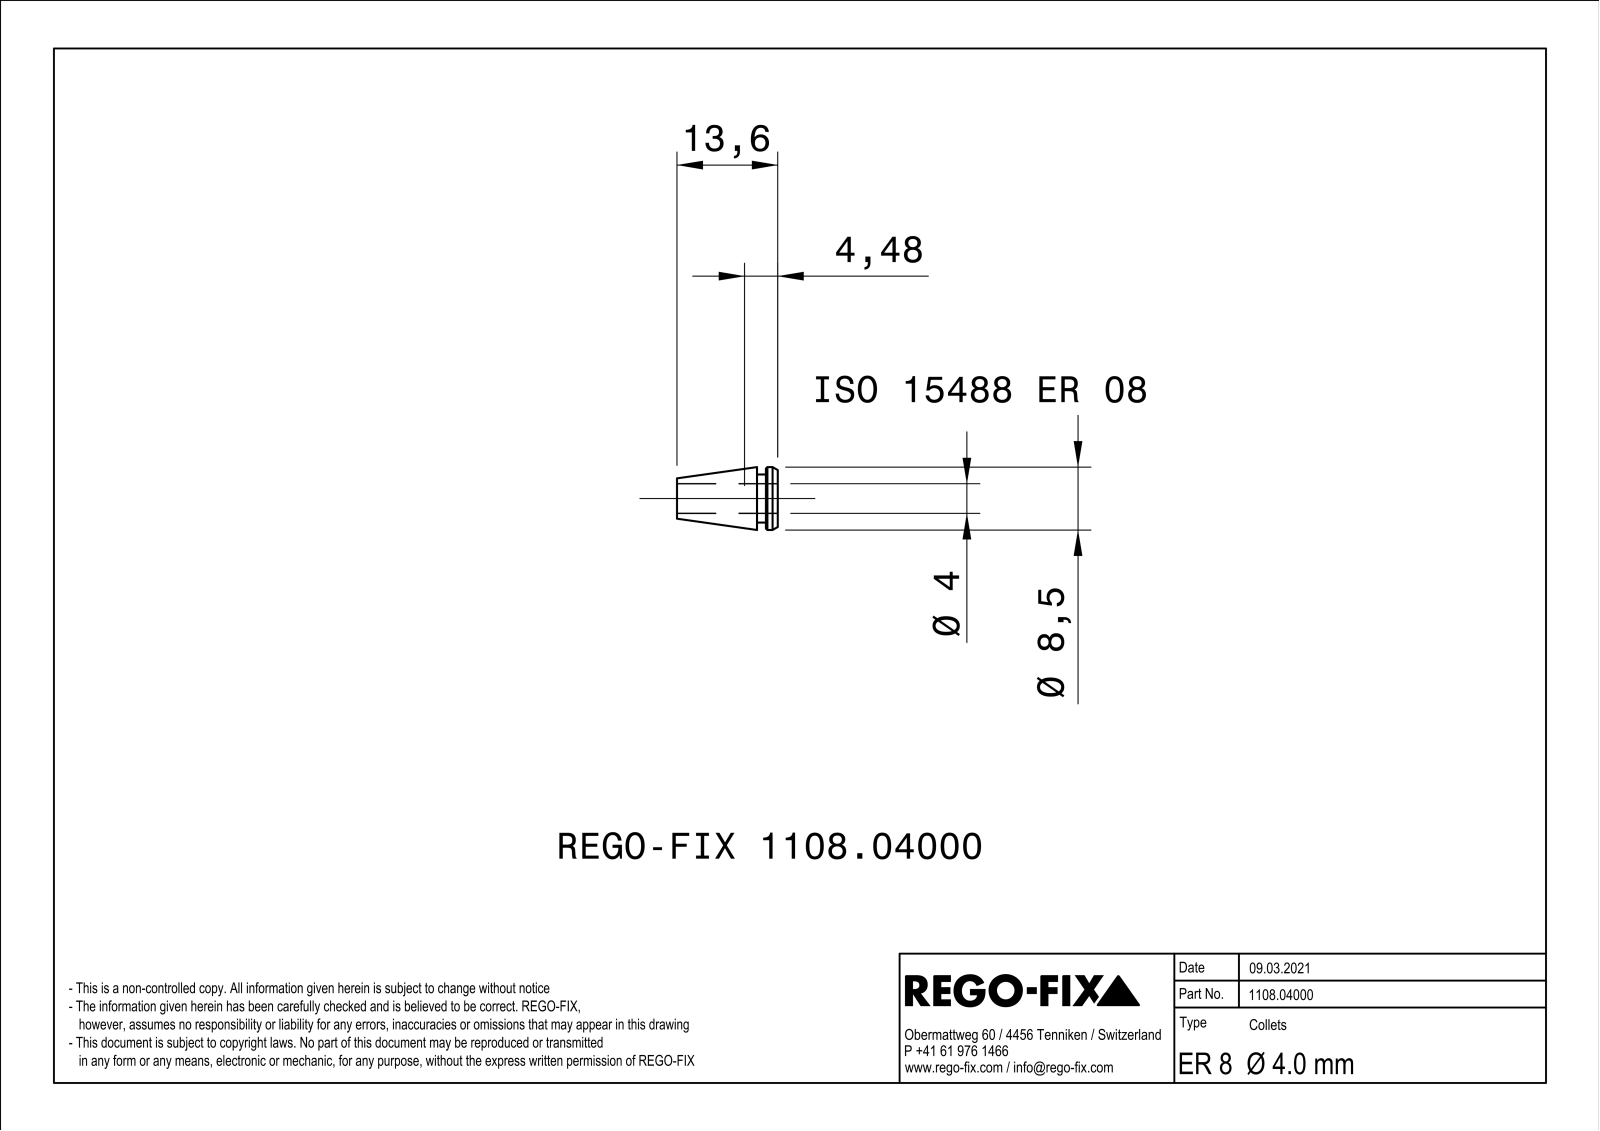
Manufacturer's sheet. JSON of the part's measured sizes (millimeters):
{"part_name": "NOCUT", "step_written_by": "SIEMENS PLM Software Solid Edge ST10 (AUTOMOTIVE_DESIGN)", "units": "millimeters", "bodies": {"solids": 1, "faces": 205, "planar": 72, "cylindrical": 49, "other": 84}, "overall_size": [13.6, 8.49, 8.49], "volume_mm3": 285, "surface_area_mm2": 889, "round_holes": [[4, 1]], "round_bosses_or_shafts": [[8.5, 1]], "partial_cylinders_radius": [[20, 12], [3.25, 1]], "face_to_face_distances": [0.4, 2.8, 1.6, 1.2, 13.6, 12, 10.8]}
